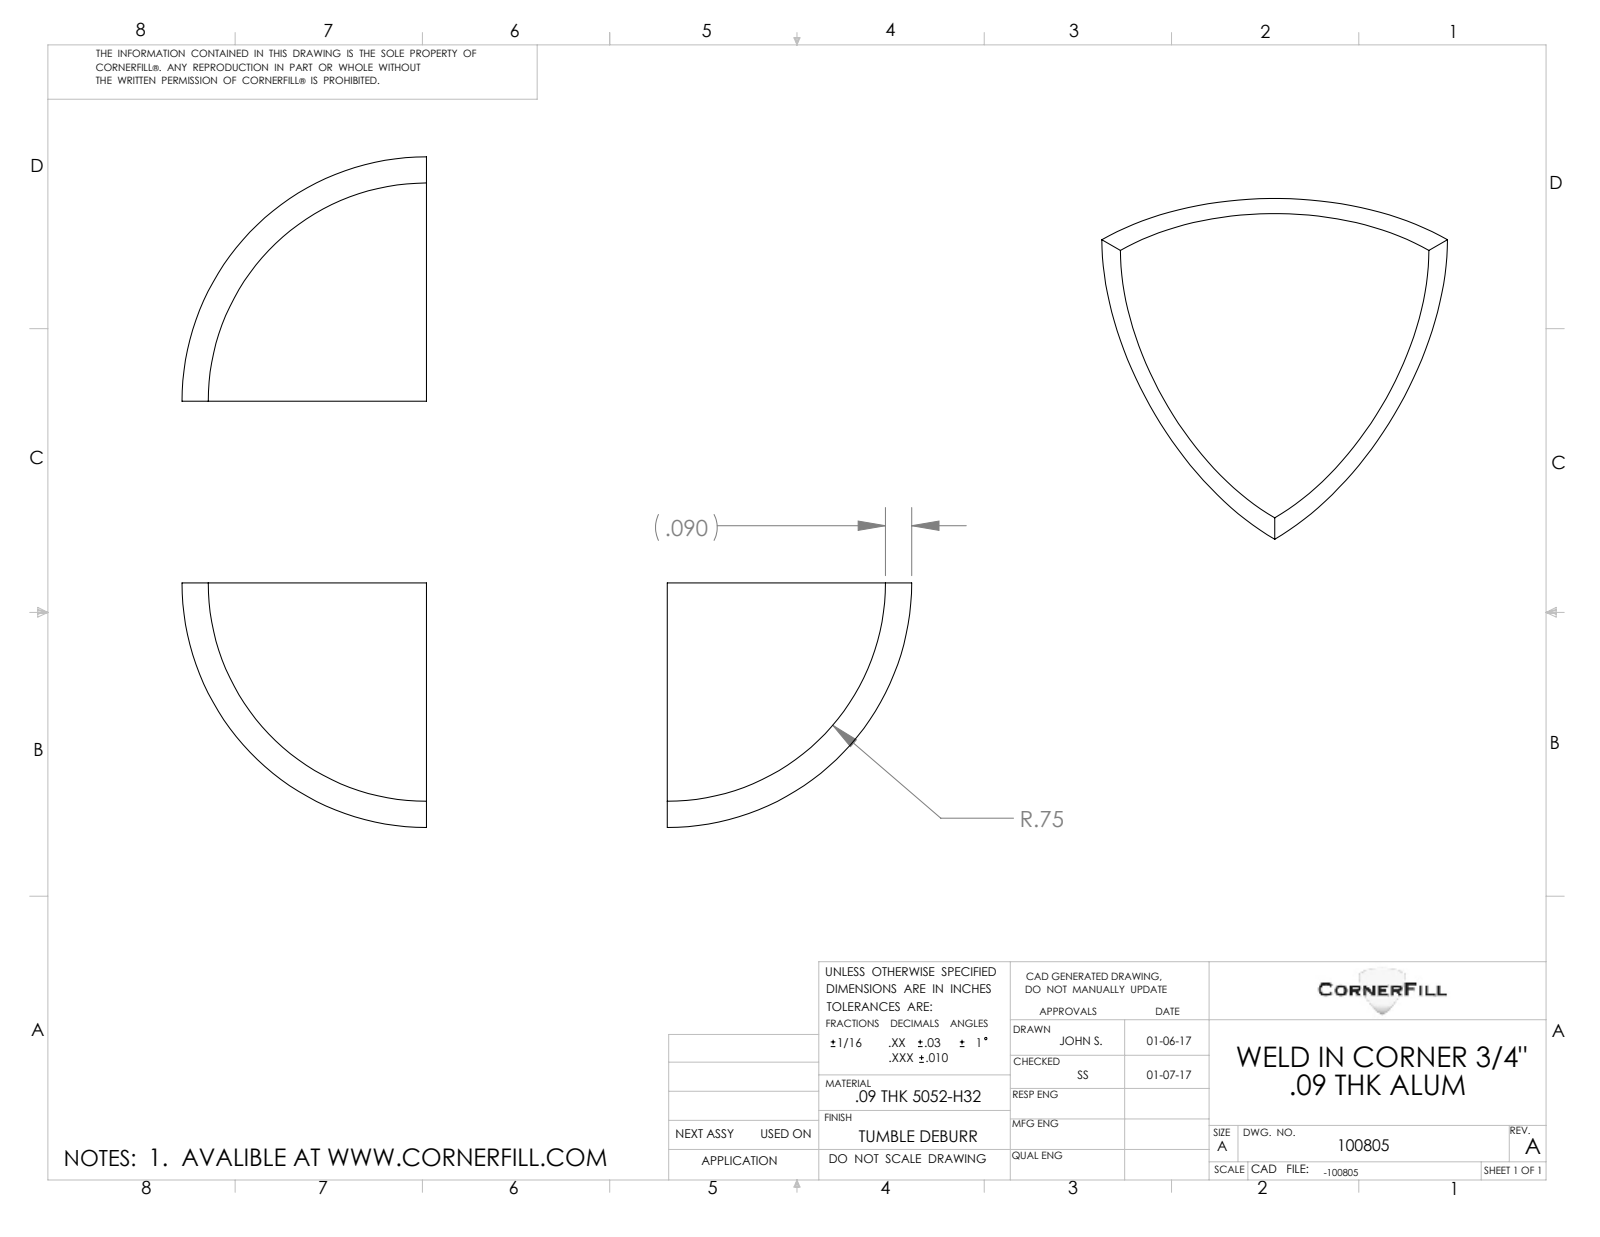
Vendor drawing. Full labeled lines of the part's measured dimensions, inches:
Part name (STEP PRODUCT): CORNERFILL# 100805
STEP written by: SolidWorks 2016 (AUTOMOTIVE_DESIGN)
Units: inches
Bodies: 1 solid, 5 faces (3 planar, 0 cylindrical, 2 other)
Overall size (bounding box): 0.84 × 0.84 × 0.84
Volume: 0.089 in³ · Surface area: 2.329 in²
